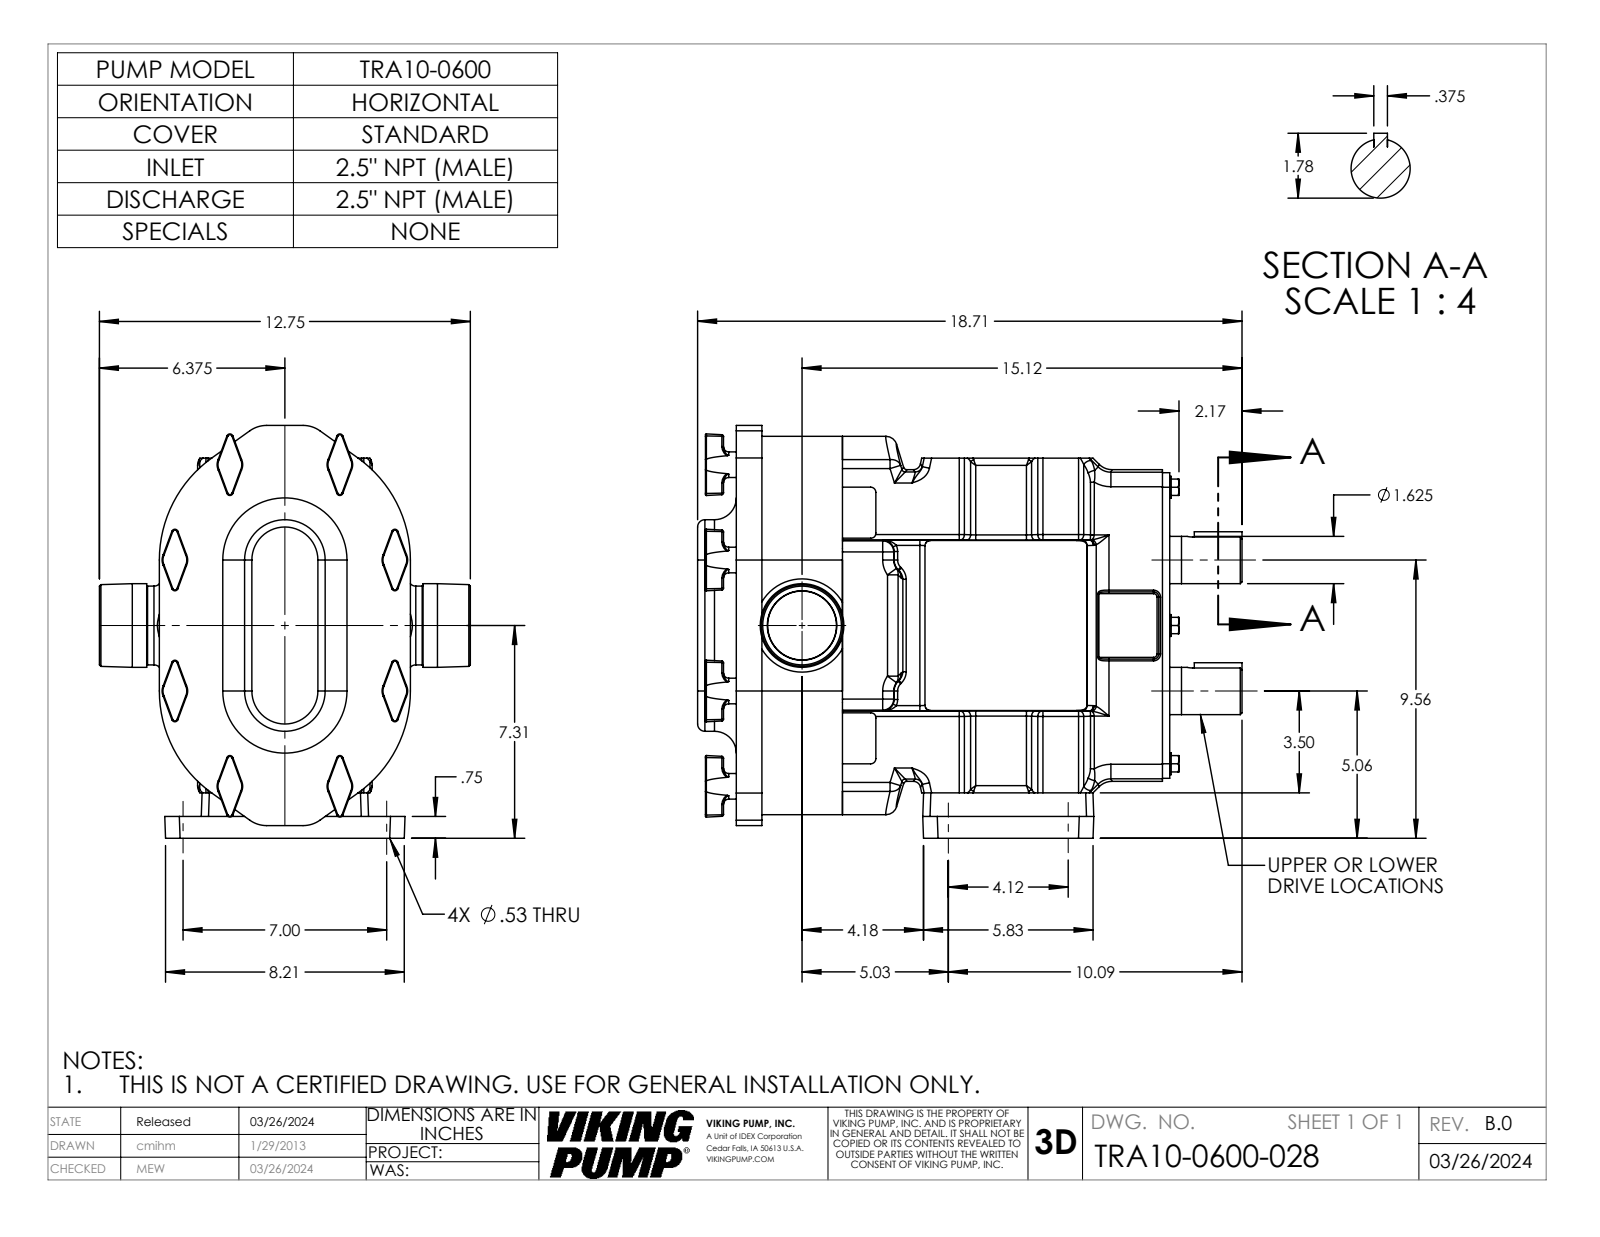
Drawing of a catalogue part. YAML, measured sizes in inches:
part_name: "TRA10-0600-028; TRA10-0600-BODY; TRA10-0600-GEARBOX-H; 0600NPT25 (+1 more)"
step_written_by: "SolidWorks 2022 (AUTOMOTIVE_DESIGN)"
units: inches
bodies: {solids: 5, faces: 1041, planar: 285, cylindrical: 368, other: 388}
overall_size: [18.714, 14.185, 12.75]
volume: 1189
surface_area: 1366
round_holes:
  - {diameter: 0.531, count: 4}
  - {diameter: 2.368, count: 1}
round_bosses_or_shafts:
  - {diameter: 0.88, count: 8}
  - {diameter: 0.75, count: 6}
  - {diameter: 1.624, count: 2}
  - {diameter: 2.875, count: 1}
  - {diameter: 2.708, count: 1}
partial_cylinders:
  - {radius: 0.18, count: 44}
  - {radius: 0.06, count: 43}
  - {radius: 0.03, count: 32}
  - {radius: 0.25, count: 32}
  - {radius: 0.38, count: 28}
  - {radius: 0.12, count: 24}
  - {radius: 0.5, count: 20}
  - {radius: 0.375, count: 12}
face_to_face_distances: [2.769, 0.5, 0.88, 3.649, 0.36, 14.899, 14.019, 11.25, 6.5, 0.86]
hole_center_spacings: [4.12, 7, 8.122]
